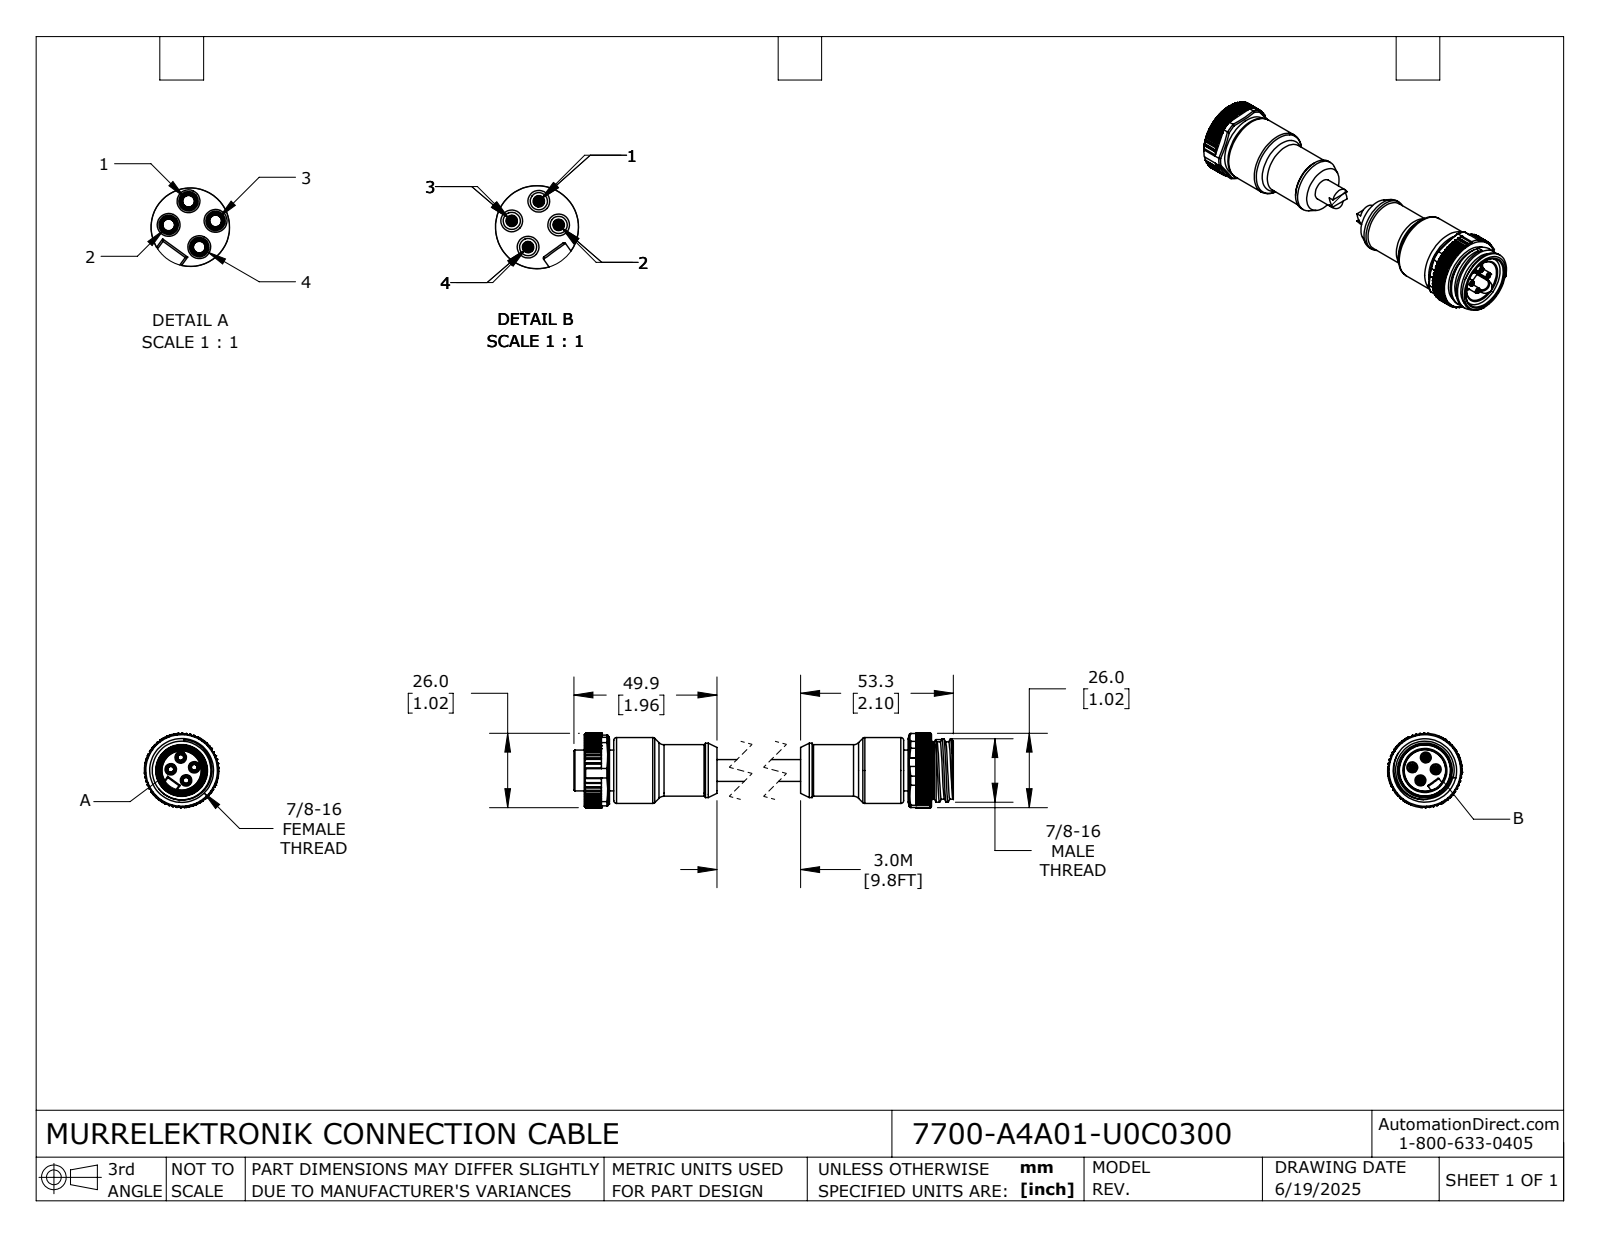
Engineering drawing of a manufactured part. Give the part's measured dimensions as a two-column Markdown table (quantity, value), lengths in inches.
| quantity | value |
| --- | --- |
| part name | 7700-A4A01-U0C0300_MALE; 7700-A4A01-U0C0300_FEMALE; 7700-A4A01-U0C0300 |
| STEP written by | SolidWorks 2024 (CONFIG_CONTROL_DESIGN) |
| units | inches |
| bodies | 2 solids, 1226 faces (520 planar, 543 cylindrical, 163 other) |
| overall size | 5.244 × 1.024 × 1.024 |
| volume | 2.059 in³ |
| surface area | 22.09 in² |
| round holes (diameter × count) | 0.081 × 4, 0.118 × 4, 0.134 × 4, 0.61 × 1, 0.614 × 1, 0.728 × 1, 0.807 × 1, 0.875 × 1 |
| round bosses / shafts (diameter × count) | 0.079 × 4, 0.906 × 1, 0.873 × 1, 0.789 × 1, 0.787 × 1, 0.748 × 1, 0.713 × 1, 0.709 × 1 |
| partial cylindrical surfaces (radius × count) | 0.008 × 252, 0.012 × 18, 0.004 × 8, 0.027 × 4, 0.029 × 4, 0.093 × 1, 0.512 × 1 |
| main face-to-face distances | 0.059, 4.075, 1.476, 2.657, 1.417, 2.598, 4.134, 0.346, 4.421, 0.287 |
| hole center spacings | 0.15, 0.324, 0.179, 0.179, 0.212, 0.213, 0.23, 0.26 |
